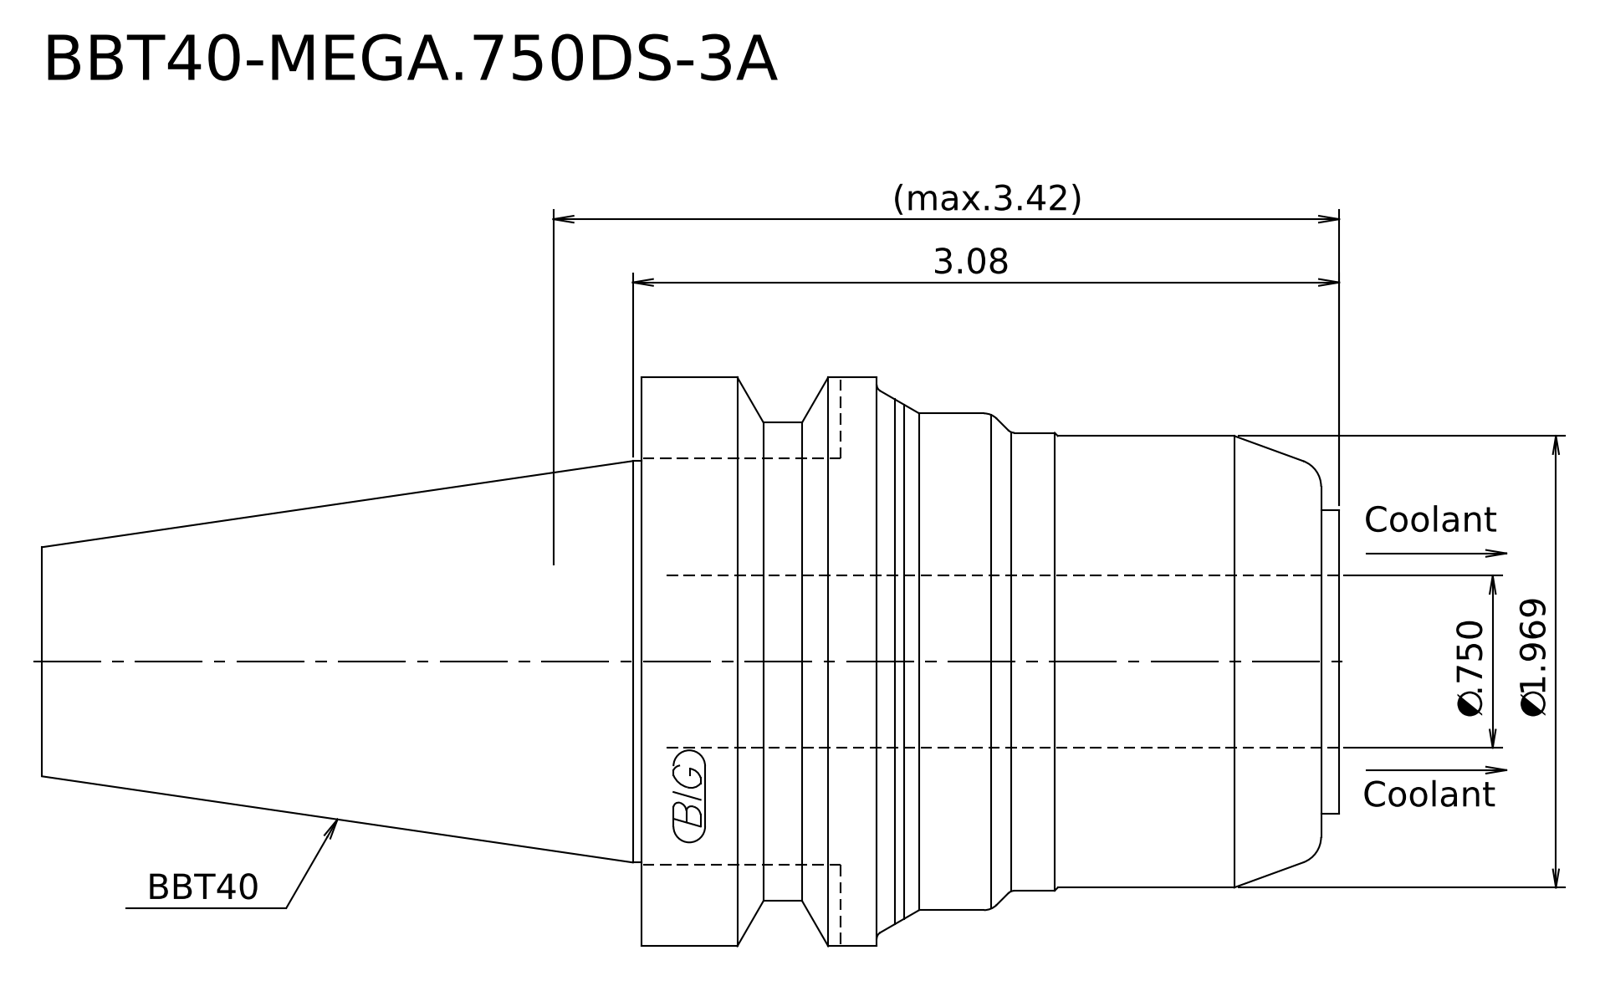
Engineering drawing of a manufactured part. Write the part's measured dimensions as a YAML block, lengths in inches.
step_written_by: "Kubotek KeyCreator 2011 V10.0.2 (22737) (automotive_design)"
units: inches
bodies: {solids: 1, faces: 22, planar: 5, cylindrical: 8, other: 9}
overall_size: [5.654, 2.48, 2.48]
volume: 14.84
surface_area: 39.68
round_bosses_or_shafts:
  - {diameter: 2.48, count: 1}
  - {diameter: 2.165, count: 1}
  - {diameter: 2.087, count: 1}
  - {diameter: 1.996, count: 1}
  - {diameter: 1.969, count: 1}
  - {diameter: 1.75, count: 1}
  - {diameter: 1.323, count: 1}
face_to_face_distances: [3.039, 0.079, 2.961, 5.654, 5.575, 2.614, 2.016, 1.937, 1.024, 3.638]
